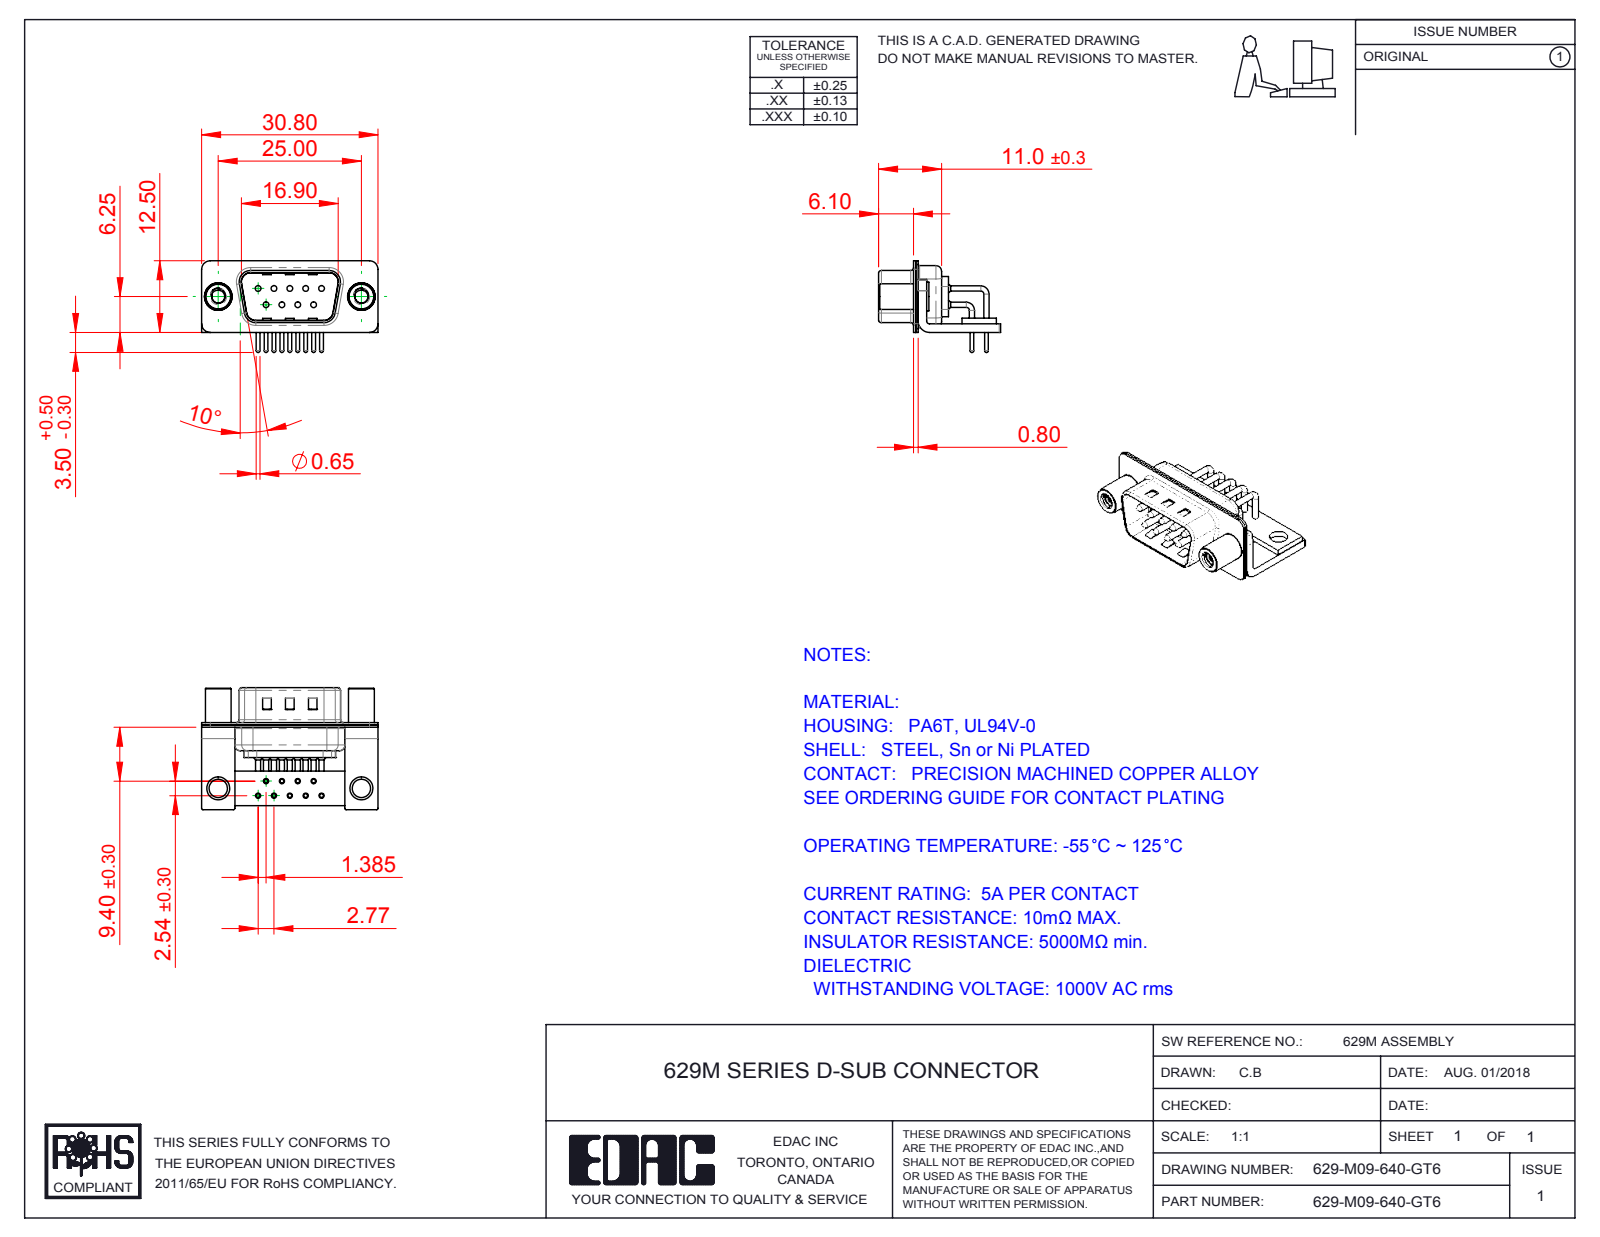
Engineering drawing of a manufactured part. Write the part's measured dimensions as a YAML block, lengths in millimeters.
part_name: "629M Shell Front_09 Contacts; 629M Shell Rear_09 Contacts; 629M Housing_09 Contacts; 629M Contact Row 1 (+5 more)"
step_written_by: "SolidWorks 2016 (CONFIG_CONTROL_DESIGN)"
units: millimeters
bodies: {solids: 17, faces: 1412, planar: 711, cylindrical: 535, other: 166}
overall_size: [30.8, 21.3, 16]
volume: 1938
surface_area: 5267
round_holes:
  - {diameter: 0.9, count: 9}
  - {diameter: 1, count: 9}
  - {diameter: 1.7, count: 9}
  - {diameter: 2, count: 9}
  - {diameter: 2.26, count: 2}
  - {diameter: 3.2, count: 2}
  - {diameter: 4, count: 2}
  - {diameter: 4.8, count: 2}
round_bosses_or_shafts:
  - {diameter: 1.5, count: 9}
  - {diameter: 0.9, count: 9}
  - {diameter: 0.65, count: 9}
  - {diameter: 5, count: 2}
  - {diameter: 4.9, count: 2}
  - {diameter: 4.5, count: 2}
partial_cylinders:
  - {radius: 0.25, count: 16}
  - {radius: 1.5, count: 16}
  - {radius: 2, count: 13}
  - {radius: 0.5, count: 9}
  - {radius: 1.01, count: 9}
  - {radius: 1.6, count: 8}
  - {radius: 0.6, count: 4}
  - {radius: 0.65, count: 4}
face_to_face_distances: [0.4, 1.5, 0.8, 0.85, 1.25, 1.9, 1, 2.5, 10.4, 9.55]
hole_center_spacings: [2.77, 5.54, 3.16, 4.87, 8.31, 2.89, 2.9, 5.03]
